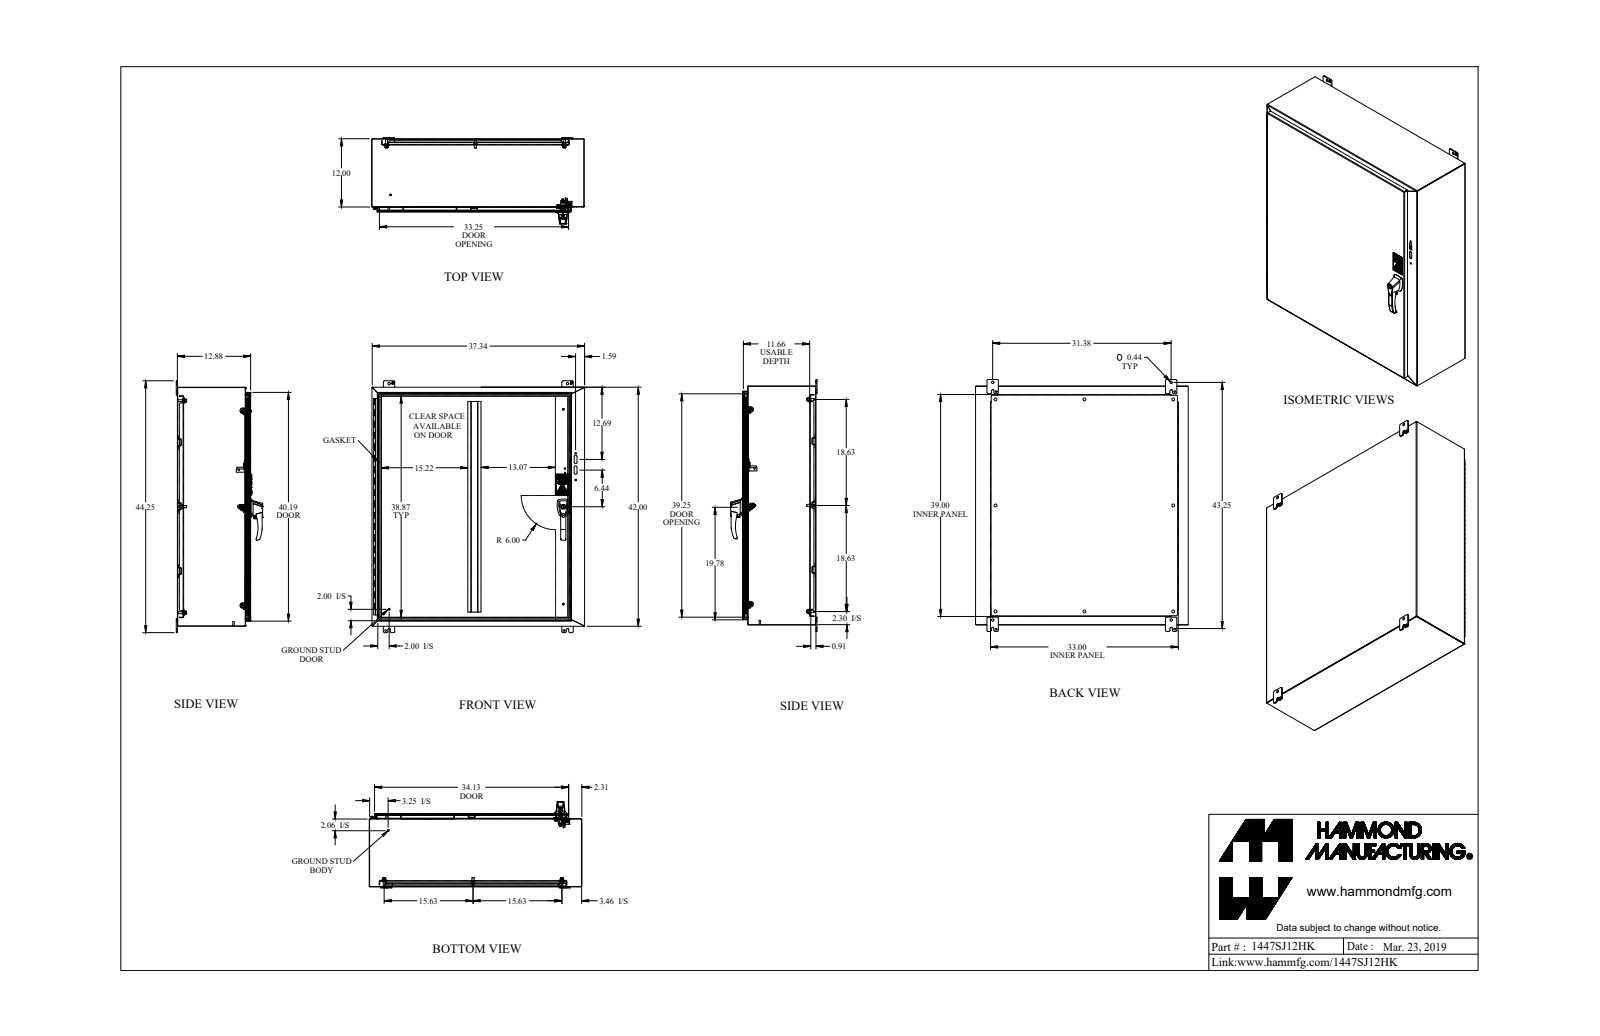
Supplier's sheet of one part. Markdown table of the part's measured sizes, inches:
| quantity | value |
| --- | --- |
| part name | 1447SJ12HK_Default |
| STEP written by | SolidWorks 2019 (CONFIG_CONTROL_DESIGN) |
| units | inches |
| bodies | 71 solids, 2015 faces (1012 planar, 800 cylindrical, 203 other) |
| overall size | 44.25 × 37.375 × 15.177 |
| volume | 583.6 in³ |
| surface area | 14 983 in² |
| round holes (diameter × count) | 0.5 × 8, 0.176 × 6, 0.313 × 6, 0.307 × 4, 0.437 × 4, 0.445 × 4, 0.25 × 3, 0.265 × 3, 0.413 × 3, 0.156 × 2, 0.173 × 2, 0.196 × 2 |
| round bosses / shafts (diameter × count) | 0.375 × 11, 0.25 × 9, 0.65 × 8, 0.33 × 8, 1 × 7, 0.156 × 6, 0.375 × 3, 0.63 × 2 |
| partial cylindrical surfaces (radius × count) | 0.25 × 35, 0.188 × 34, 0.036 × 18, 0.108 × 18, 0.116 × 16, 0.125 × 16, 0.03 × 10, 0.218 × 8 |
| main face-to-face distances | 0.072, 12.803, 12.731, 12.875, 0.095, 11.771, 11.699, 1.032, 1.104, 11.866 |
| hole center spacings | 31.25, 31.375, 1.11, 15.625, 18.625, 24.311, 30.193, 36.379 |
